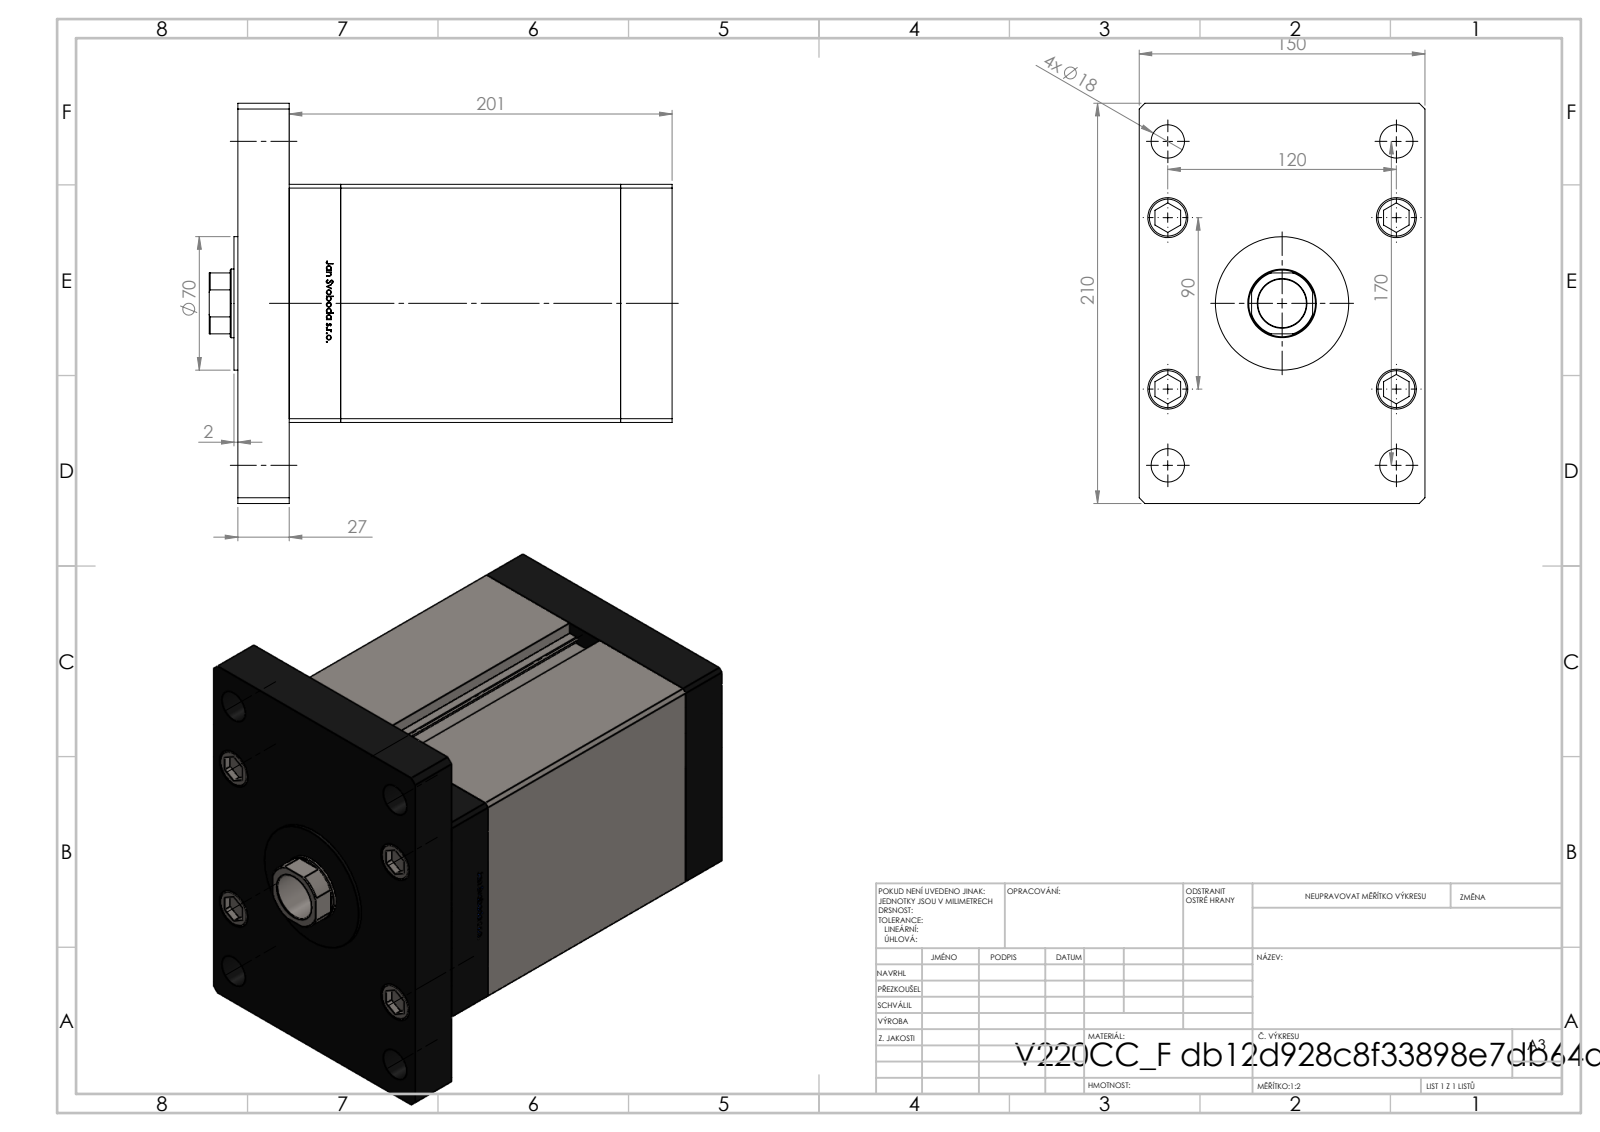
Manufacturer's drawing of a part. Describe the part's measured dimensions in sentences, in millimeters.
The part is named "V220C_VC_F; V220C_FRONT_F; ALLEN BOLT; V220C_F (+2 more)". Its 3-D file was written by "SolidWorks 2019 (CONFIG_CONTROL_DESIGN)". It is 19 solids with 1298 faces: 513 planar, 179 cylindrical and 606 other. Overall it measures 243 by 210 by 150 millimeters. Its volume is 4 076 000 cubic millimeters and its surface area 452 115 square millimeters. Round holes: 9 of diameter 17.5, 5 of diameter 22, 4 of diameter 16, 4 of diameter 21, 1 of diameter 25.5, 1 of diameter 36, 1 of diameter 37.5. Round bosses or shafts: 9 of diameter 8, 5 of diameter 21, 1 of diameter 80, 1 of diameter 70. Partial cylindrical surfaces (rounded edges, fillets, slot ends): 2 of radius 0.93, 1 of radius 17.5. The main face-to-face distances are 27, 174, 201, 150, 147, 54, 125, 167.5, 228, 33.5. The hole center spacings are 51, 40, 75, 104.04, 120, 126.49, 130, 176.92.
